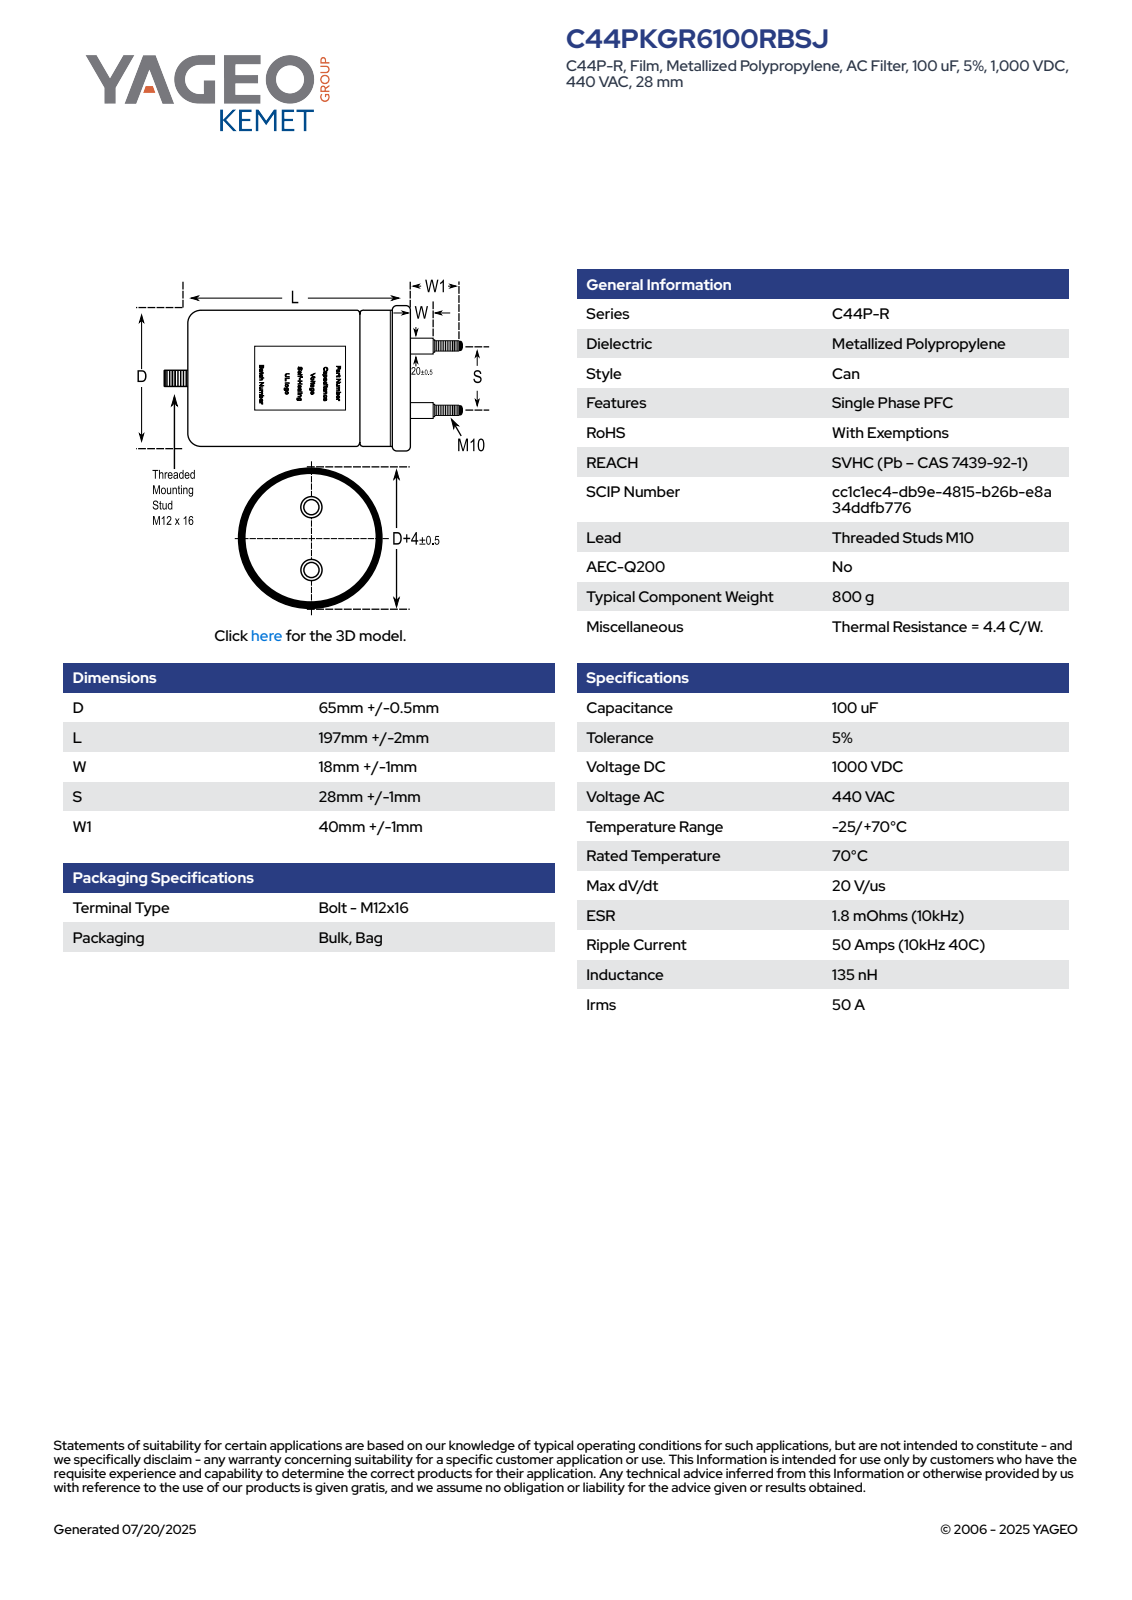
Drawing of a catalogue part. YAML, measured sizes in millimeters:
part_name: "CFP_C44P_65X197_D65.5L199S28"
step_written_by: "SolidWorks 2014 (AUTOMOTIVE_DESIGN)"
units: millimeters
bodies: {solids: 1, faces: 105, planar: 32, cylindrical: 36, other: 37}
overall_size: [256, 70, 70]
volume: 689817
surface_area: 52476
round_bosses_or_shafts:
  - {diameter: 12, count: 3}
  - {diameter: 20.5, count: 2}
  - {diameter: 10, count: 2}
  - {diameter: 70, count: 1}
  - {diameter: 65.5, count: 1}
partial_cylinders:
  - {radius: 32.76, count: 1}
face_to_face_distances: [199, 217, 18, 192.61, 6.39, 24.39, 240, 47.39, 41, 23]
